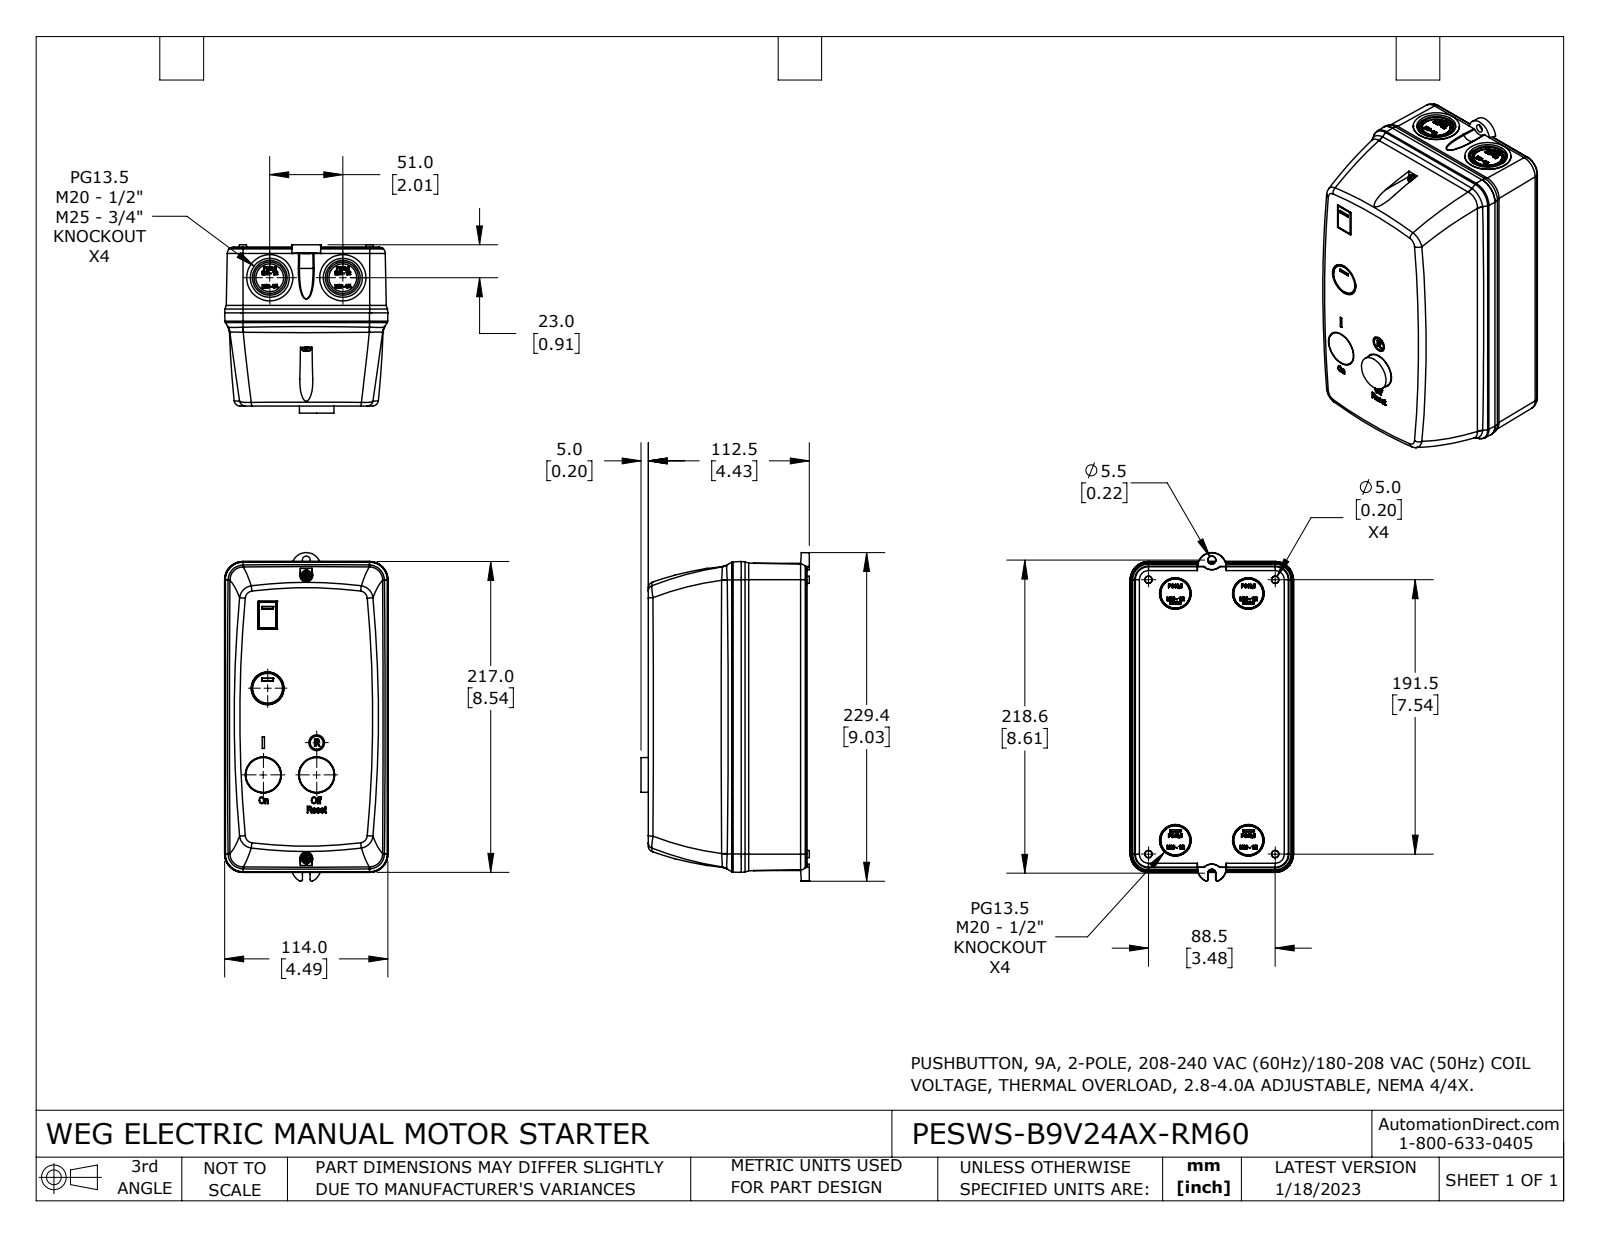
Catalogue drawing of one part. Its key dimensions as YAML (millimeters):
part_name: "PESWS-B9V24AX-RM60"
step_written_by: "SolidWorks 2021 (CONFIG_CONTROL_DESIGN)"
units: millimeters
bodies: {solids: 6, faces: 2195, planar: 1110, cylindrical: 92, other: 993}
overall_size: [229.44, 117.5, 114.01]
volume: 2457000
surface_area: 166196
round_holes:
  - {diameter: 4.4, count: 2}
  - {diameter: 21.91, count: 2}
  - {diameter: 27.24, count: 2}
  - {diameter: 5.5, count: 1}
  - {diameter: 11, count: 1}
round_bosses_or_shafts:
  - {diameter: 32.26, count: 2}
  - {diameter: 24.25, count: 2}
  - {diameter: 24.2, count: 2}
  - {diameter: 19.37, count: 2}
  - {diameter: 7, count: 2}
  - {diameter: 3, count: 2}
  - {diameter: 9, count: 1}
partial_cylinders:
  - {radius: 2, count: 4}
  - {radius: 4.61, count: 4}
  - {radius: 9.54, count: 4}
  - {radius: 6.54, count: 2}
  - {radius: 7.54, count: 2}
  - {radius: 2.08, count: 1}
  - {radius: 2.17, count: 1}
  - {radius: 2.75, count: 1}
face_to_face_distances: [46, 65, 111, 0.5, 110.5, 45.5, 110, 1, 109.5, 64]
hole_center_spacings: [10.5, 51, 81.32, 117.22, 127.71, 198, 208.5]
